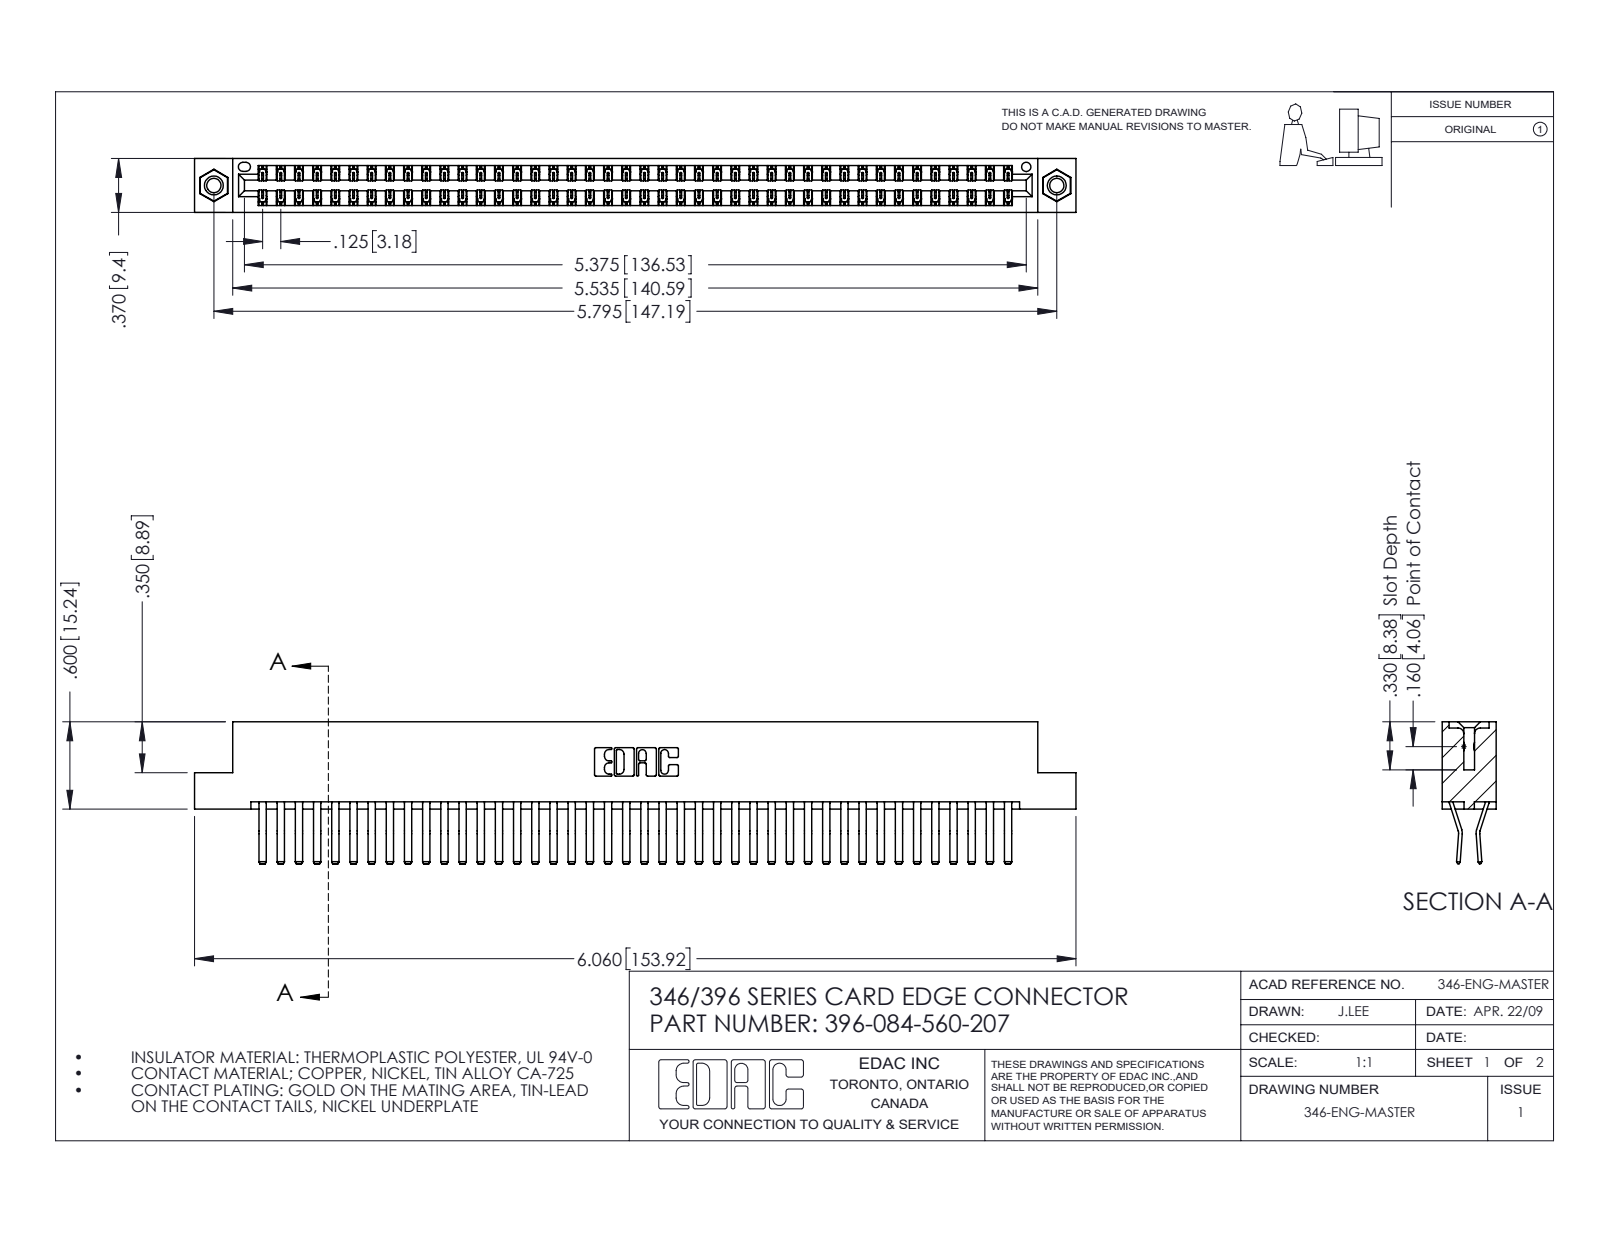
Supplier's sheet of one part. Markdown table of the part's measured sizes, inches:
| quantity | value |
| --- | --- |
| part name | 345-250-001_345-250-005-103; 345-292-001_560 Tail; 396-084-560-207; 346 Part_Flush Mounting Lugs - 0.156 Dia-TI |
| STEP written by | SolidWorks 2016 (CONFIG_CONTROL_DESIGN) |
| units | inches |
| bodies | 87 solids, 4718 faces (3048 planar, 1654 cylindrical, 16 other) |
| overall size | 6.06 × 0.975 × 0.37 |
| volume | 0.949 in³ |
| surface area | 35.45 in² |
| round holes (diameter × count) | 0.098 × 2, 0.125 × 2, 0.156 × 2, 0.064 × 1 |
| round bosses / shafts (diameter × count) | 0.155 × 2 |
| partial cylindrical surfaces (radius × count) | 0.006 × 126, 0.01 × 22, 0.007 × 6, 0.031 × 6, 0.026 × 3, 0.01 × 2, 0.014 × 2, 0.022 × 2 |
| main face-to-face distances | 0.048, 0.322, 0.37, 0.025, 0.25, 0.072, 0.298, 0.275, 0.148, 0.222 |
| hole center spacings | 0.246, 5.586, 5.795 |
